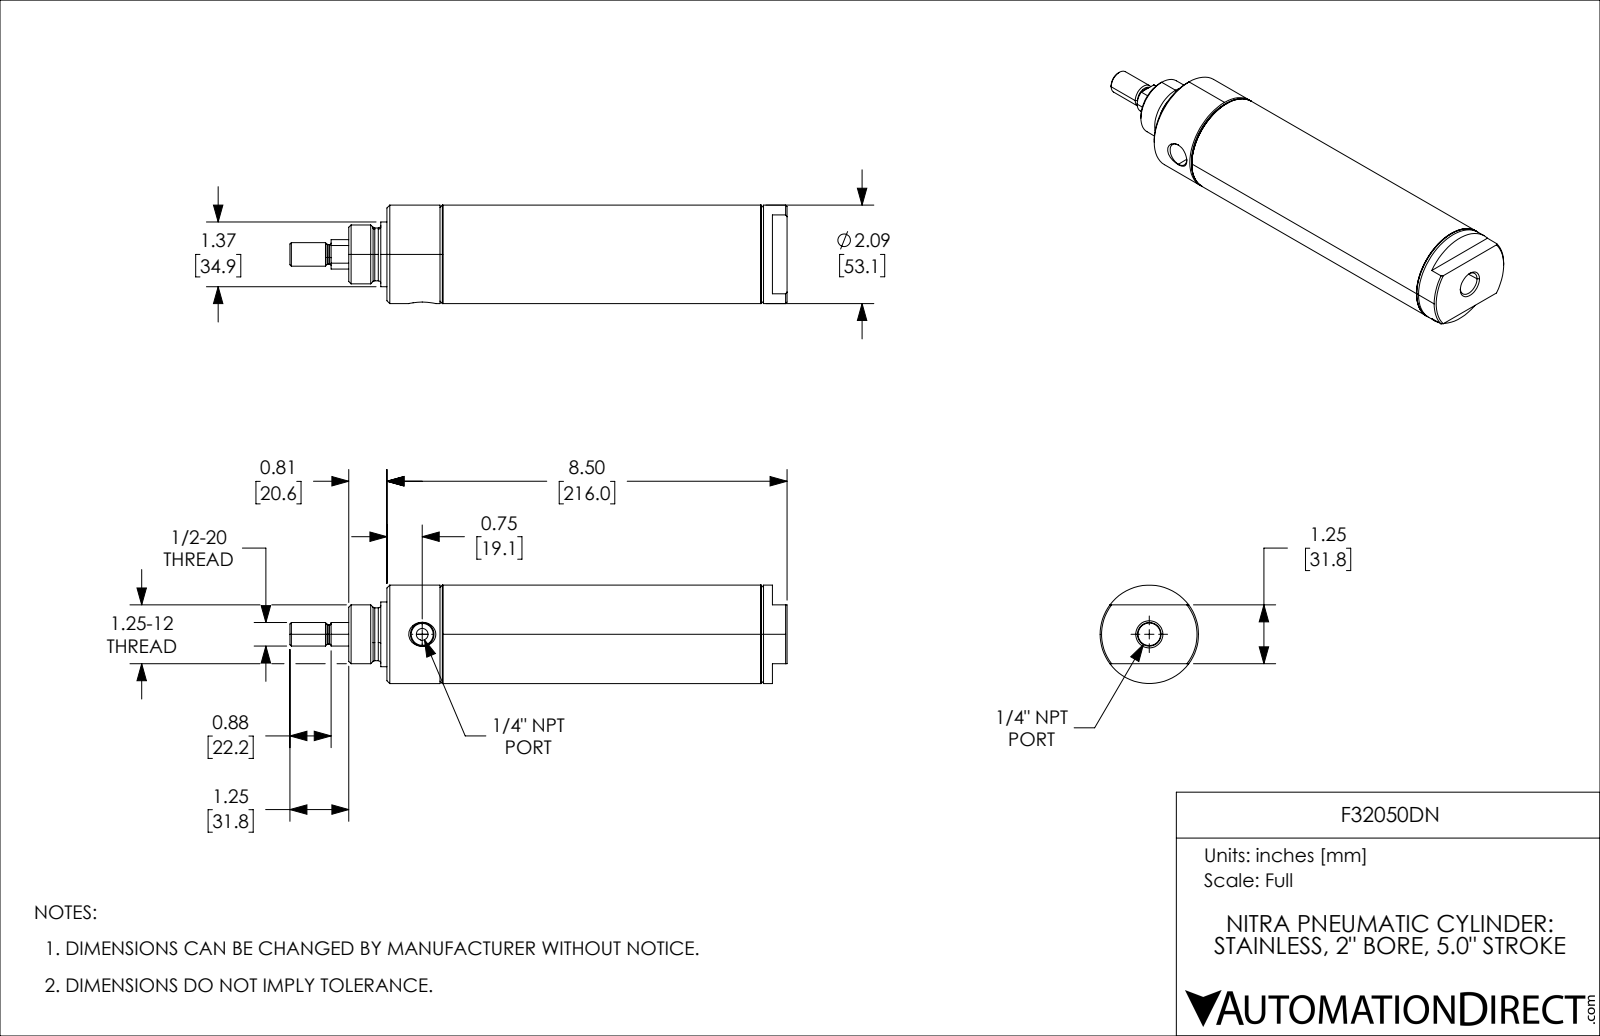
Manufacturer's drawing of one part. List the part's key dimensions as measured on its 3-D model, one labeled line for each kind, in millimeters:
Part name (STEP PRODUCT): F32050DN_5; F32050DN_3; F32050DN_9; F32050DN (+1 more)
STEP written by: SolidWorks 2021 (CONFIG_CONTROL_DESIGN)
Units: millimetres
Bodies: 4 solids, 133 faces (25 planar, 46 cylindrical, 62 other)
Overall size (bounding box): 268.27 × 53.09 × 53.09
Volume: 246 194 mm³ · Surface area: 103 207 mm²
Round holes (diameter × count): ⌀6.35 ×1, ⌀12.18 ×1, ⌀16.52 ×1, ⌀31.75 ×1, ⌀49.05 ×1
Round bosses / shafts (diameter × count): ⌀53.09 ×1, ⌀51.16 ×1, ⌀34.87 ×1, ⌀28.51 ×1, ⌀15.88 ×1, ⌀12.7 ×1, ⌀10.46 ×1
Main face-to-face distances: 30.18, 127, 157.18, 177.8, 50.8, 20.62, 38.15, 165.15, 195.33, 215.95
